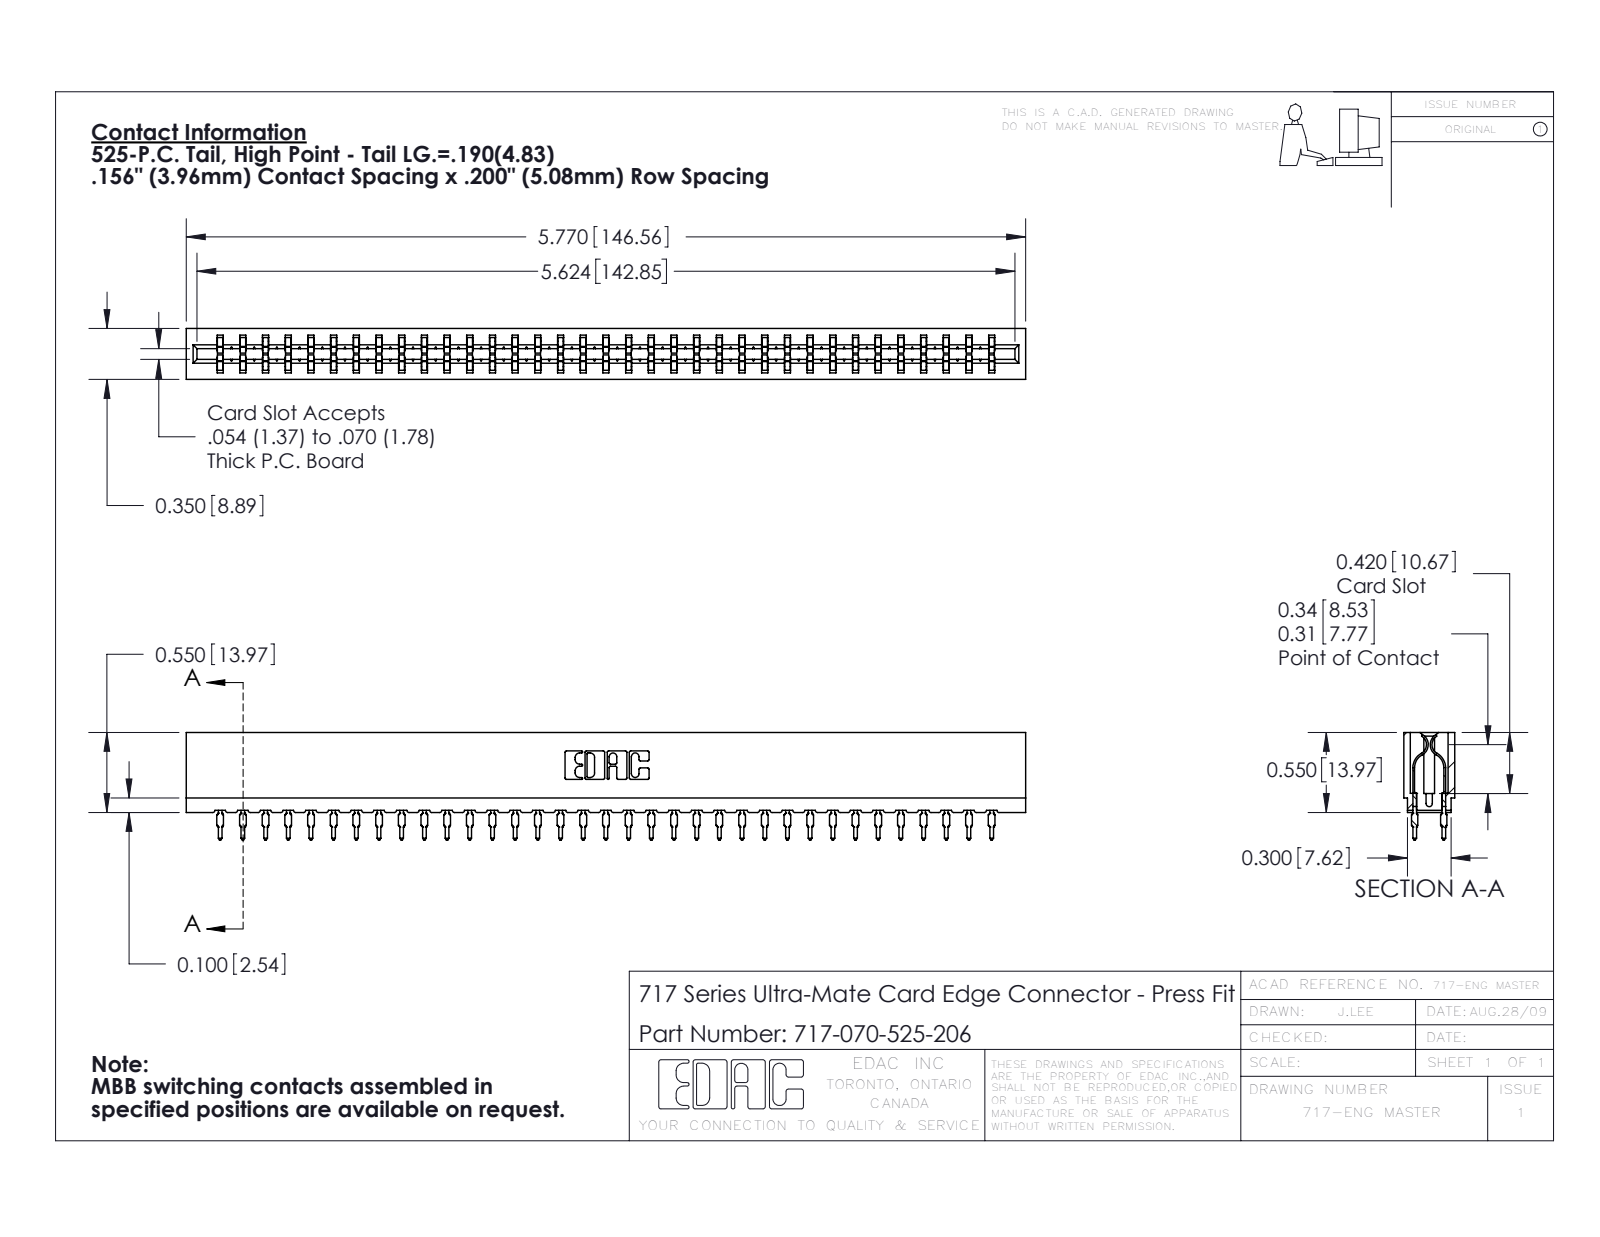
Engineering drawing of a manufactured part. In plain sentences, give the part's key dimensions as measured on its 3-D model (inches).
The part is named "717-070-525-206; 717 Part_Insulator Option - 06; 745-292-001_525". Its 3-D file was written by "SolidWorks 2016 (CONFIG_CONTROL_DESIGN)". It is 71 solids with 6394 faces: 3309 planar, 1265 cylindrical and 1820 other. Overall it measures 5.77 by 0.739 by 0.35 inches. Its volume is 0.776 cubic inches and its surface area 29.87 square inches. Partial cylindrical surfaces (rounded edges, fillets, slot ends): 140 of radius 0.021, 70 of radius 0.015, 22 of radius 0.01, 8 of radius 0.005, 8 of radius 0.011, 6 of radius 0.007, 6 of radius 0.031, 3 of radius 0.026. The main face-to-face distances are 0.212, 0.138, 0.35, 0.063, 0.287, 0.076, 0.149, 0.074, 0.045, 0.305.
